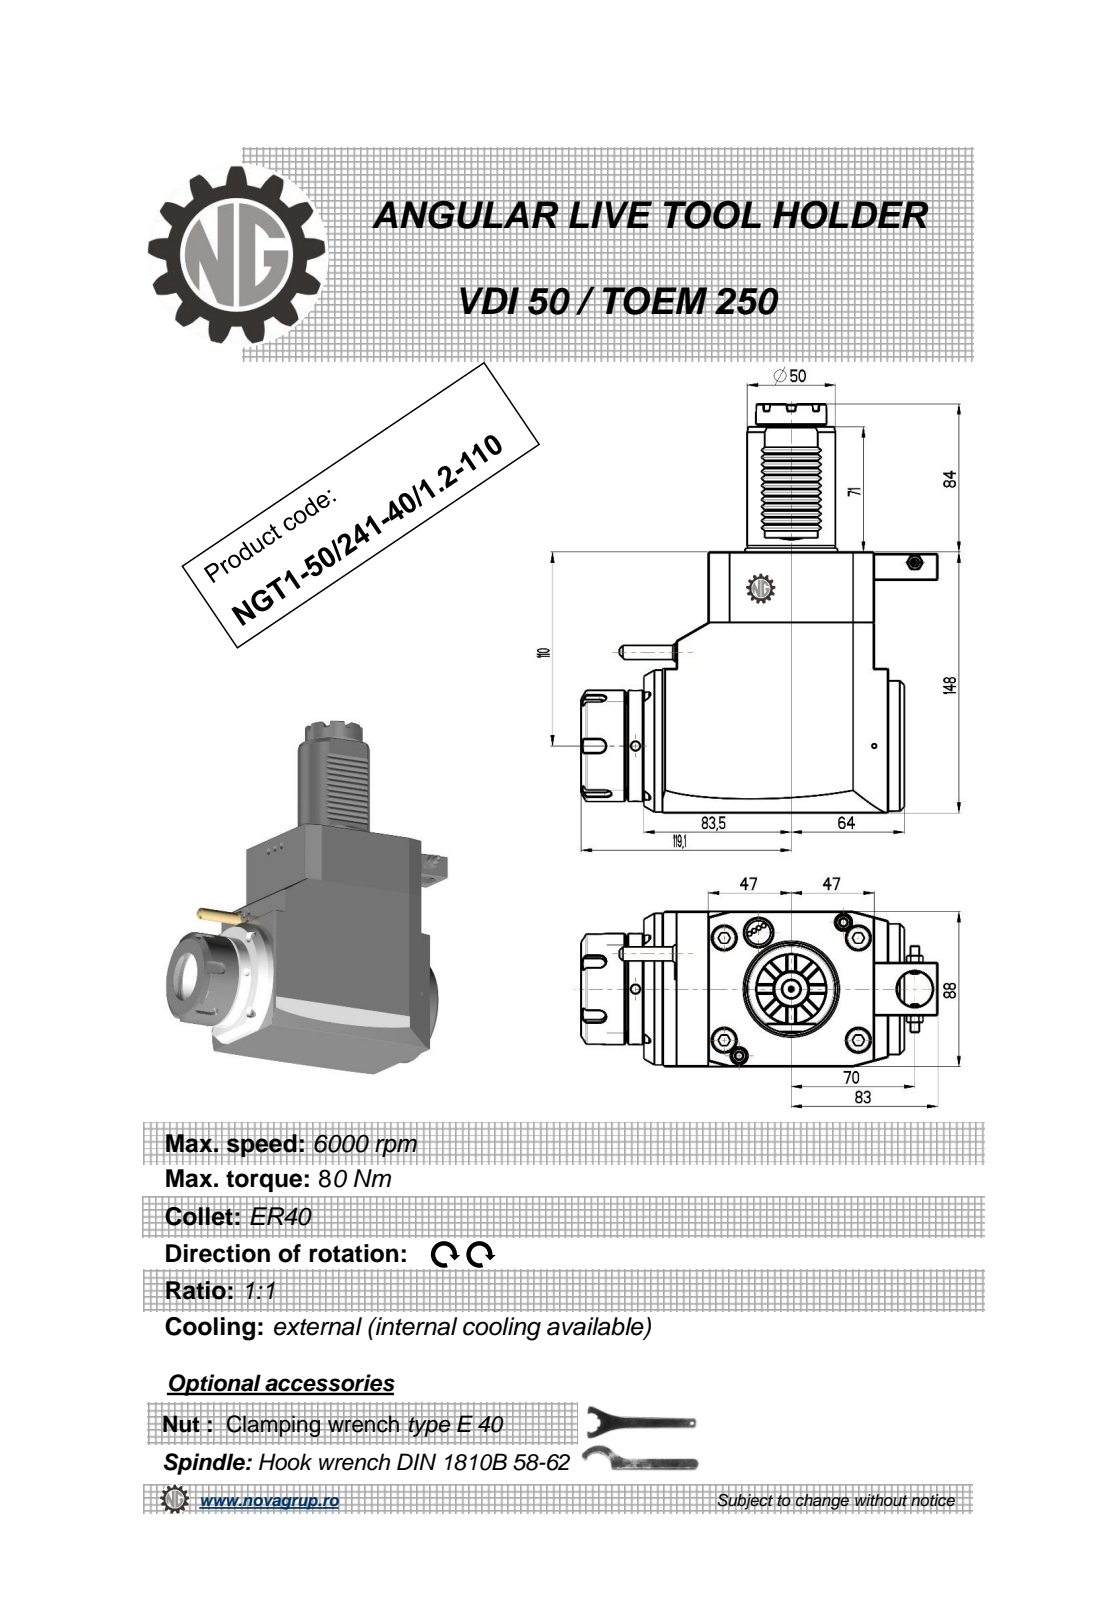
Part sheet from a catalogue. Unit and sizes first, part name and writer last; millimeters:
Units: millimetres
Overall size (bounding box): 232 × 202.1 × 88
Round holes (diameter × count): ⌀5 ×3, ⌀3 ×1, ⌀4.5 ×1, ⌀9.5 ×1, ⌀20 ×1, ⌀33.5 ×1
Round bosses / shafts (diameter × count): ⌀86 ×1, ⌀74 ×1, ⌀63 ×1, ⌀51 ×1, ⌀50 ×1, ⌀40 ×1, ⌀20.5 ×1, ⌀10 ×1
Partial cylindrical surfaces — rounded edges, fillets, slot ends (radius × count): R0.26 ×12, R0.3 ×12, R0.2 ×6, R3.75 ×5
Main face-to-face distances: 88, 148, 147.5, 8, 17, 9, 111, 94, 36.5, 130.5
Hole centre spacings: 52.46, 56.65, 101.5, 158.25
Volume: 1 838 000 mm³ · Surface area: 116 521 mm²
Bodies: 1 solid, 494 faces (245 planar, 94 cylindrical, 155 other)
Part name (STEP PRODUCT): NGT1_50_241_40_1_2_110
STEP written by: PRO/ENGINEER BY PARAMETRIC TECHNOLOGY CORPORATION, 2010280 (CONFIG_CONTROL_DESIGN)
